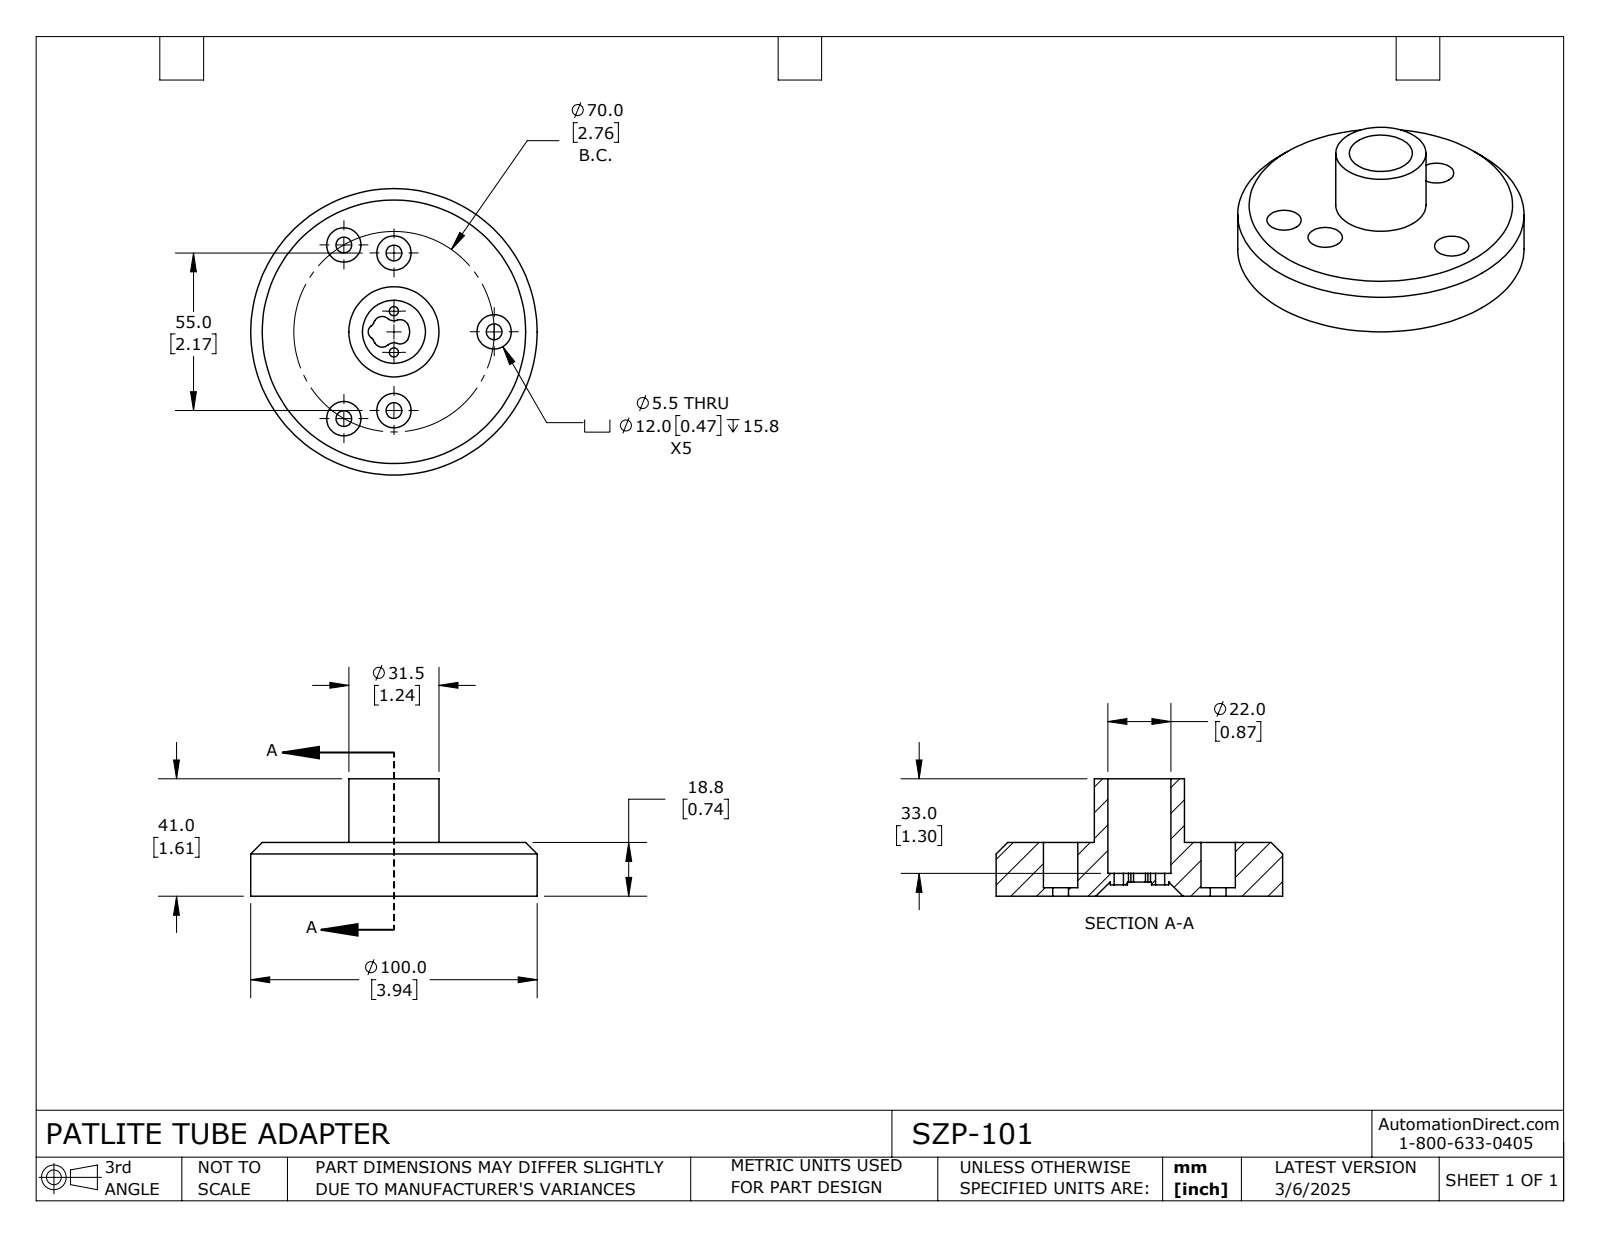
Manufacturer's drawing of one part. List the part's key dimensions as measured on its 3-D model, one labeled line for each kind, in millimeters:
Part name (STEP PRODUCT): SZP-101
STEP written by: SolidWorks 2024 (CONFIG_CONTROL_DESIGN)
Units: millimetres
Bodies: 1 solid, 66 faces (12 planar, 50 cylindrical, 4 other)
Overall size (bounding box): 100 × 100 × 41
Volume: 137 740 mm³ · Surface area: 28 483 mm²
Round holes (diameter × count): ⌀5.5 ×5, ⌀12 ×5, ⌀3.2 ×2, ⌀22 ×1
Round bosses / shafts (diameter × count): ⌀6 ×2, ⌀100 ×1, ⌀31.5 ×1
Partial cylindrical surfaces — rounded edges, fillets, slot ends (radius × count): R3 ×4, R2 ×2, R3.35 ×2, R2.5 ×1, R5.5 ×1, R7.75 ×1
Main face-to-face distances: 18.8, 3, 15.8, 5, 41, 38, 22.2, 8, 10.8, 33
Hole centre spacings: 35, 60.62, 7.2, 17.72, 20.3, 27.5, 28.99, 34.7
